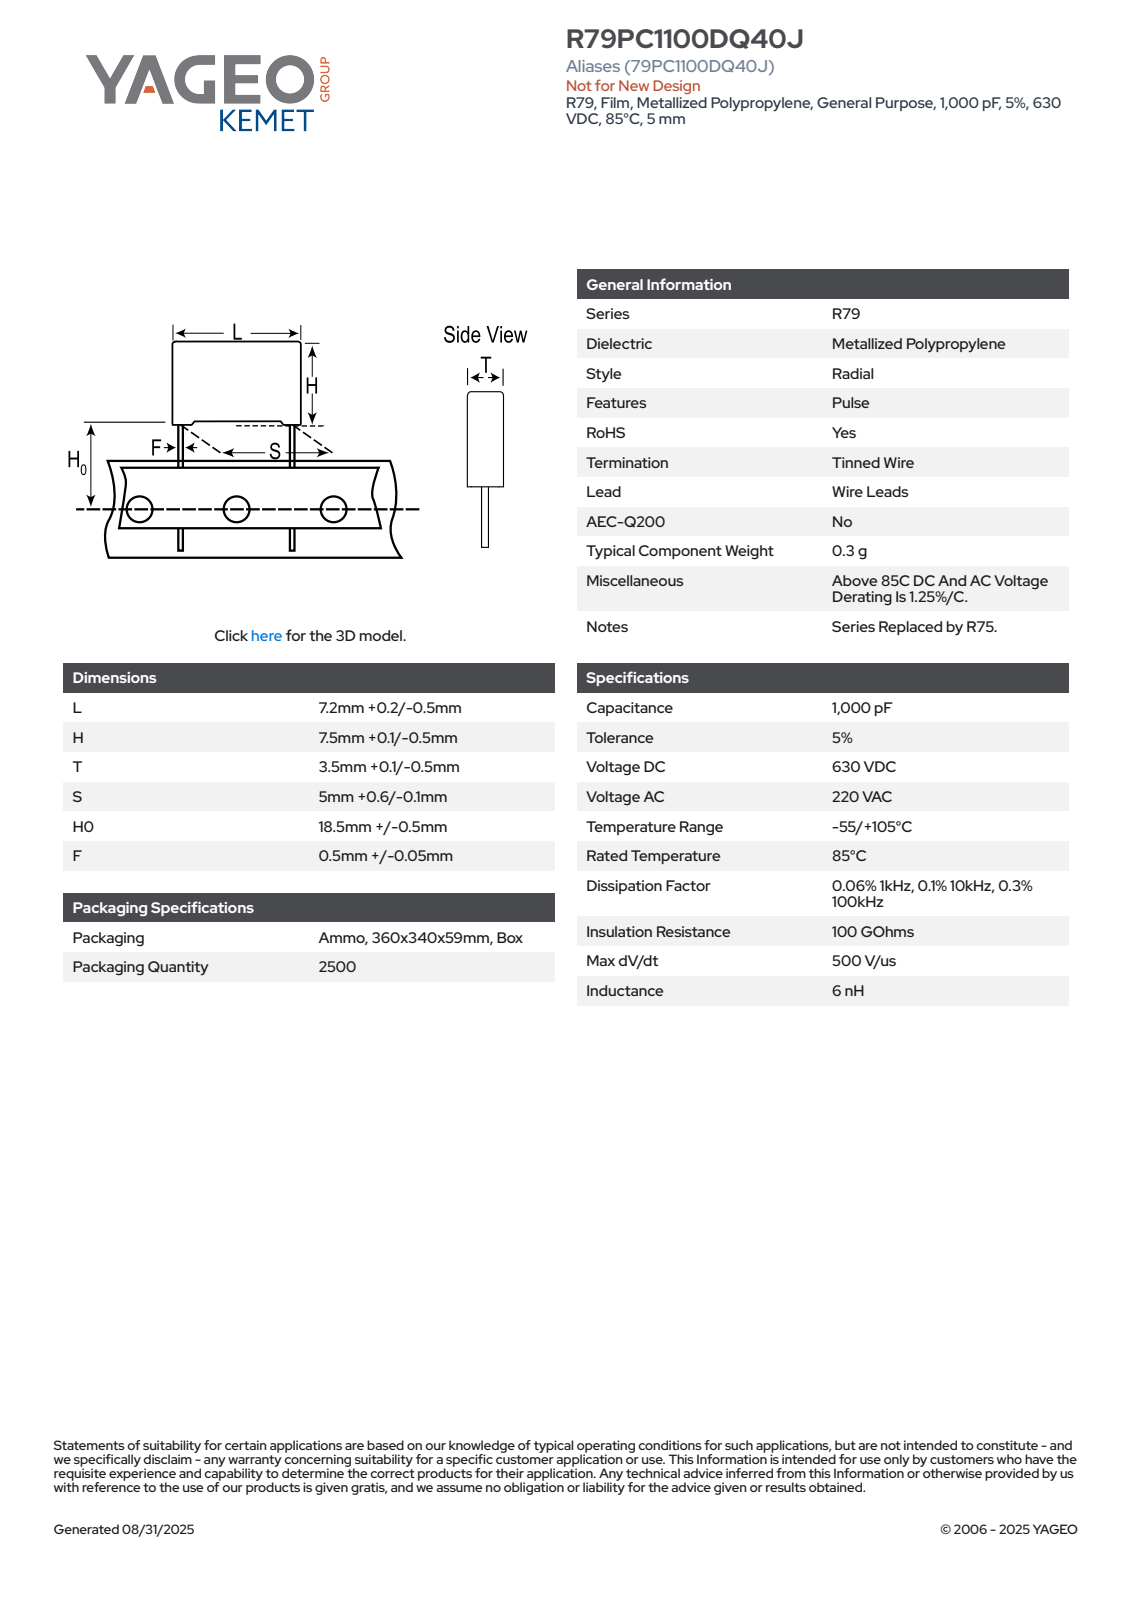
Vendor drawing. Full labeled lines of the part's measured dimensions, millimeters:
Part name (STEP PRODUCT): CFR_RB2_7.2X7.5X3.5_L7.4H7.6T3.6S5H019F0.55
STEP written by: SolidWorks 2020 (AUTOMOTIVE_DESIGN)
Units: millimetres
Bodies: 4 solids, 85 faces (77 planar, 8 cylindrical, 0 other)
Overall size (bounding box): 26.6 × 7.4 × 3.6
Volume: 194 mm³ · Surface area: 301 mm²
Round bosses / shafts (diameter × count): ⌀0.55 ×2
Partial cylindrical surfaces — rounded edges, fillets, slot ends (radius × count): R0.5 ×4
Main face-to-face distances: 3.6, 7.4, 6.85, 3.35, 3.1, 7.15, 0.75, 7.6, 6.9, 0.49
